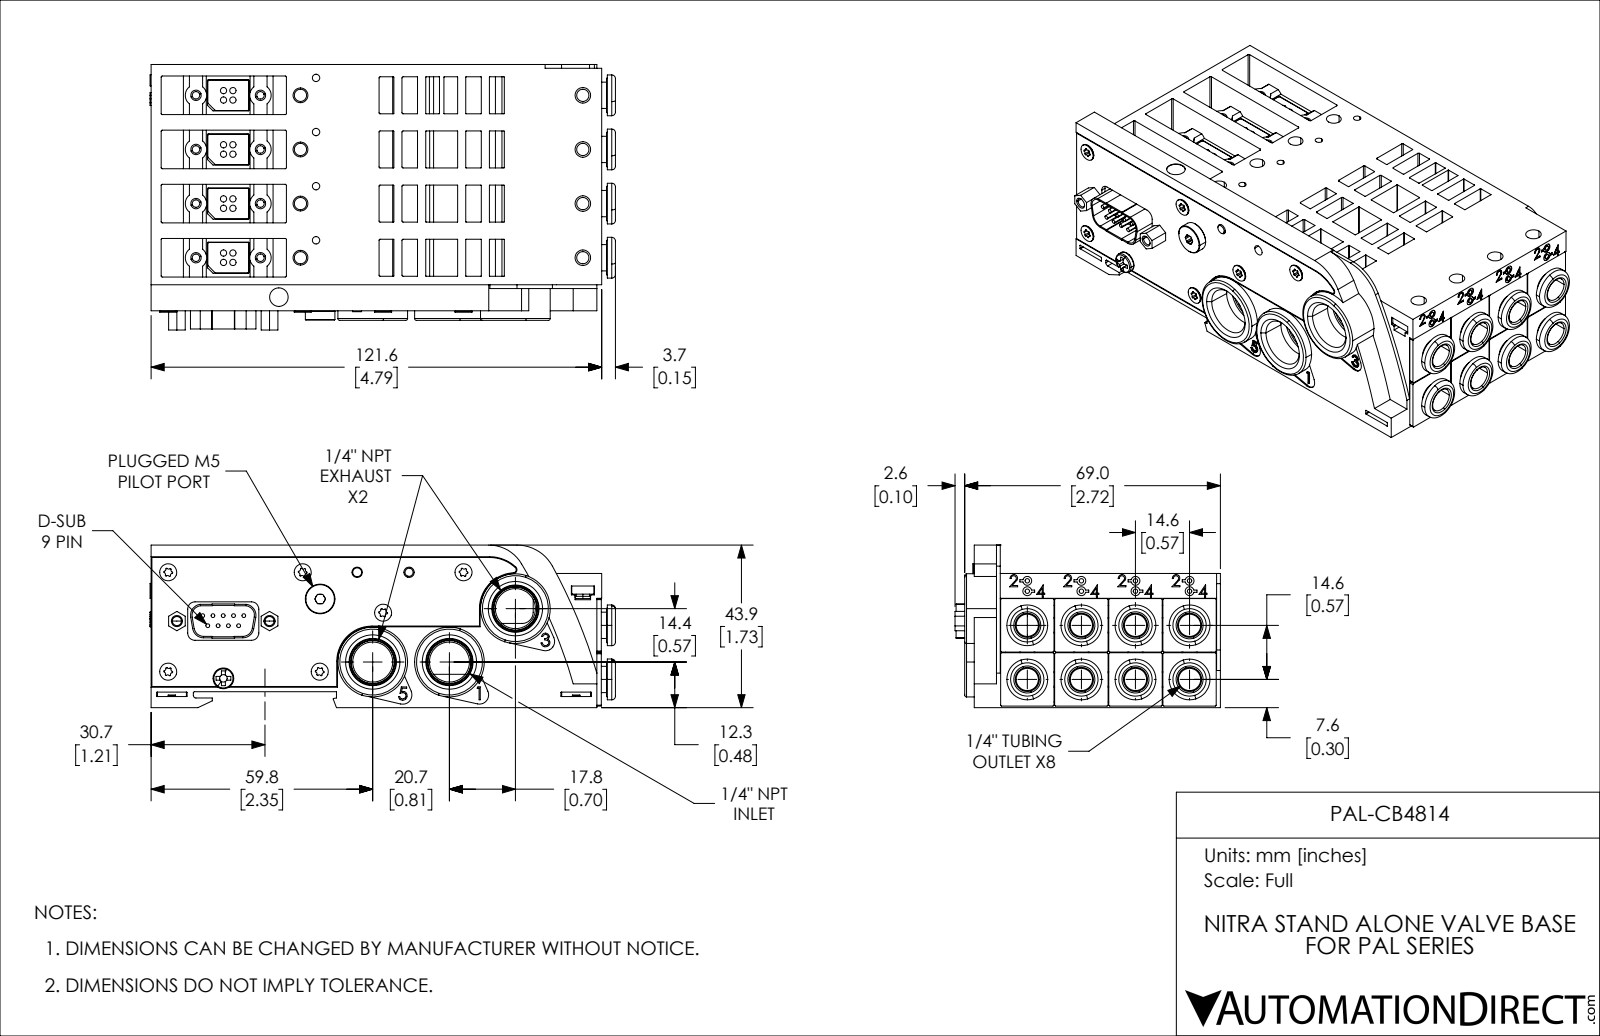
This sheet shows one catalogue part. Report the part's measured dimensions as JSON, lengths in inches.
{"part_name": "PAL-CB4814", "step_written_by": "SolidWorks 2019 (CONFIG_CONTROL_DESIGN)", "units": "inches", "bodies": {"solids": 9, "faces": 2152, "planar": 1002, "cylindrical": 934, "other": 216}, "overall_size": [4.945, 2.819, 1.727], "volume_in3": 13.95, "surface_area_in2": 126.6, "round_holes": [[0.067, 16], [0.079, 12], [0.524, 11], [0.197, 9], [0.236, 9], [0.094, 8], [0.13, 8], [0.256, 8], [0.157, 6], [0.165, 4], [0.425, 3], [0.457, 3]], "round_bosses_or_shafts": [[0.04, 9], [0.516, 8], [0.453, 8], [0.433, 8], [0.429, 8], [0.374, 8], [0.354, 8], [0.335, 8]], "partial_cylinders_radius": [[0.012, 105], [0.004, 73], [0.007, 36], [0.023, 36], [0.008, 34], [0.079, 8], [0.114, 8], [0.118, 8]], "face_to_face_distances": [1.425, 0.575, 0.252, 0.169, 1.256, 2.614, 0.087, 0.165, 1.15, 0.677], "hole_center_spacings": [0.575, 1.15, 0.1, 0.297, 0.396, 0.583, 0.601, 0.656]}
